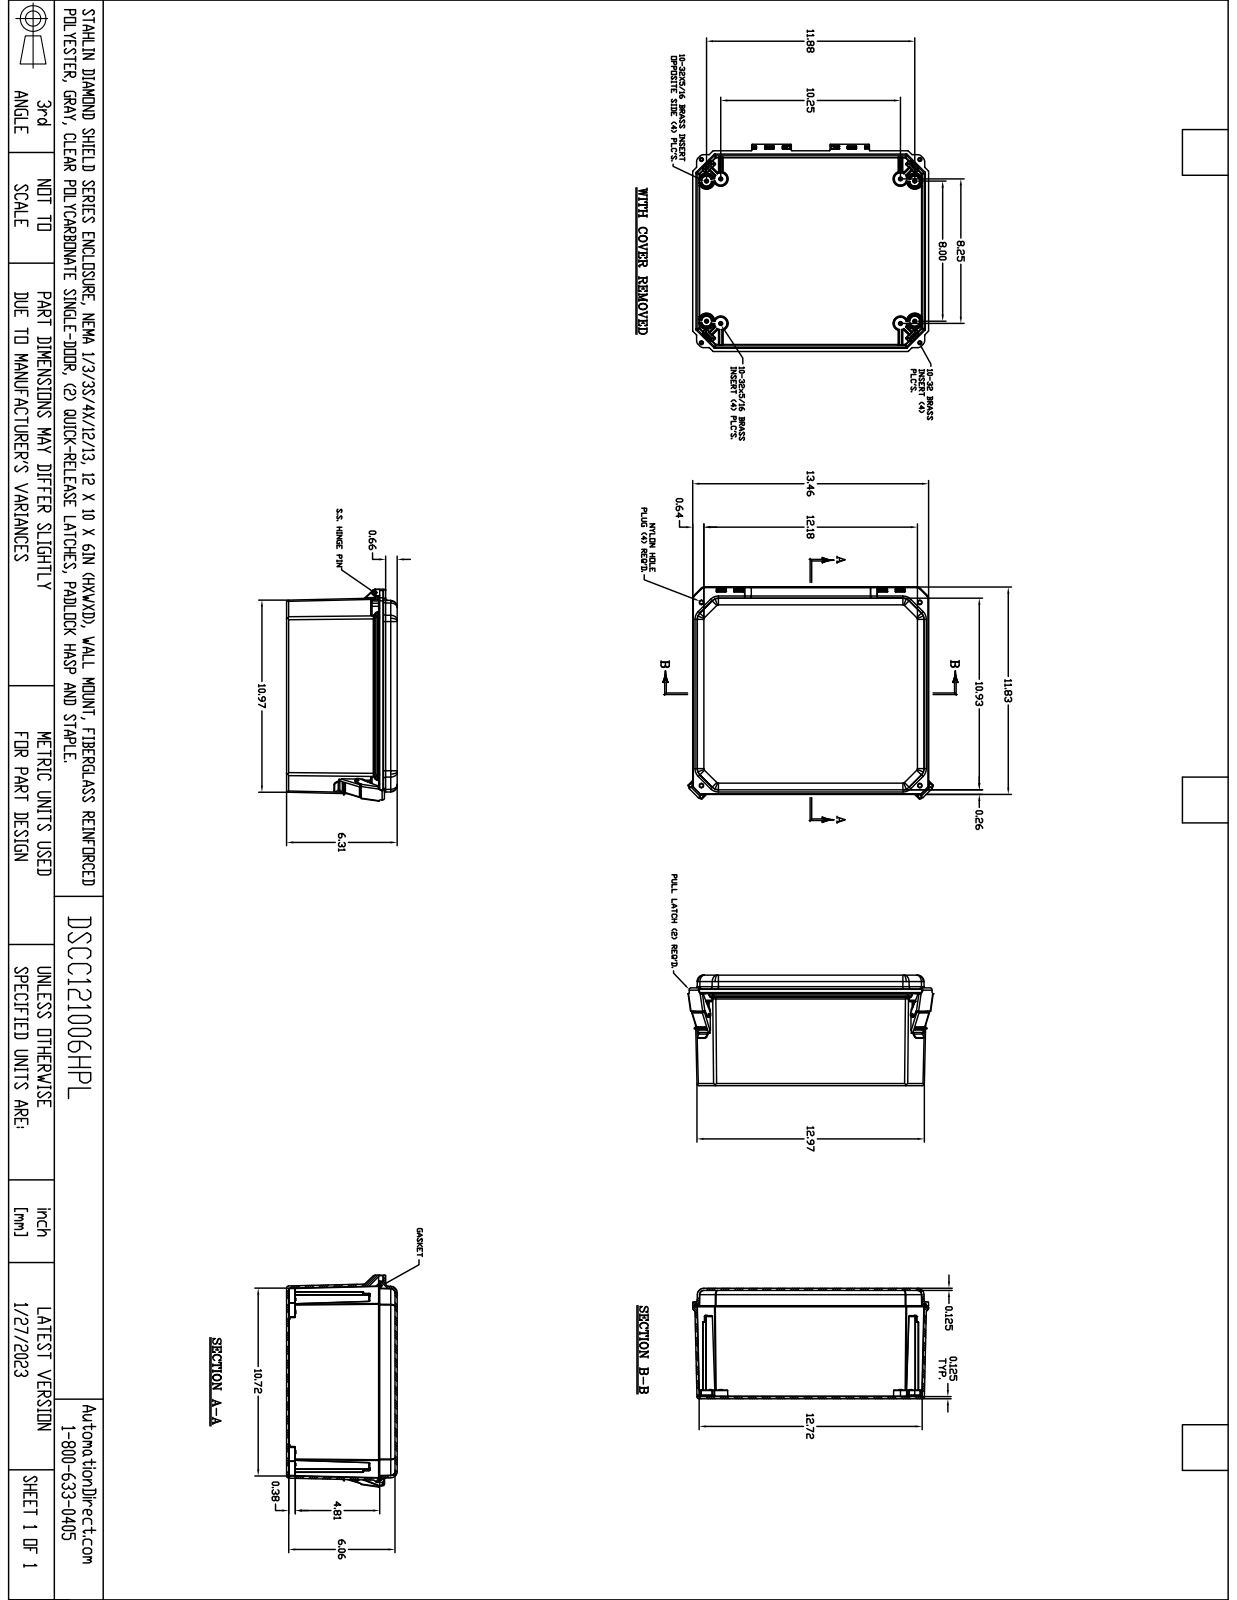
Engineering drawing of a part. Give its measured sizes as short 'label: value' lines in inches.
name: FRCC121006HPL
written by: SolidWorks 2018 (AUTOMOTIVE_DESIGN)
unit: in
bodies: 29 solids, 2205 faces (661 planar, 878 cylindrical, 666 other)
size: 14.118 × 12.165 × 6.312
volume: 83.75 in³; area: 1 268 in²
holes: 12× ⌀0.156, 8× ⌀0.152, 5× ⌀0.135, 4× ⌀0.15, 4× ⌀0.219, 4× ⌀0.252, 4× ⌀0.312, 2× ⌀0.135, 2× ⌀0.137, 2× ⌀0.375
bosses: 12× ⌀0.246, 4× ⌀0.87, 4× ⌀0.209, 4× ⌀0.135, 2× ⌀0.3
rounds: 188× R0.01, 94× R0.005, 59× R0.02, 58× R0.03, 29× R0.125, 26× R0.09, 24× R0.03, 24× R0.06
face distances: 0.125, 6.187, 6.062, 6.312, 0.139, 0.14, 0.14, 5.531, 0.656, 1
hole spacings: 1.261, 9.231, 0.25, 11.406, 0.824, 1.559, 8.165, 9.417
